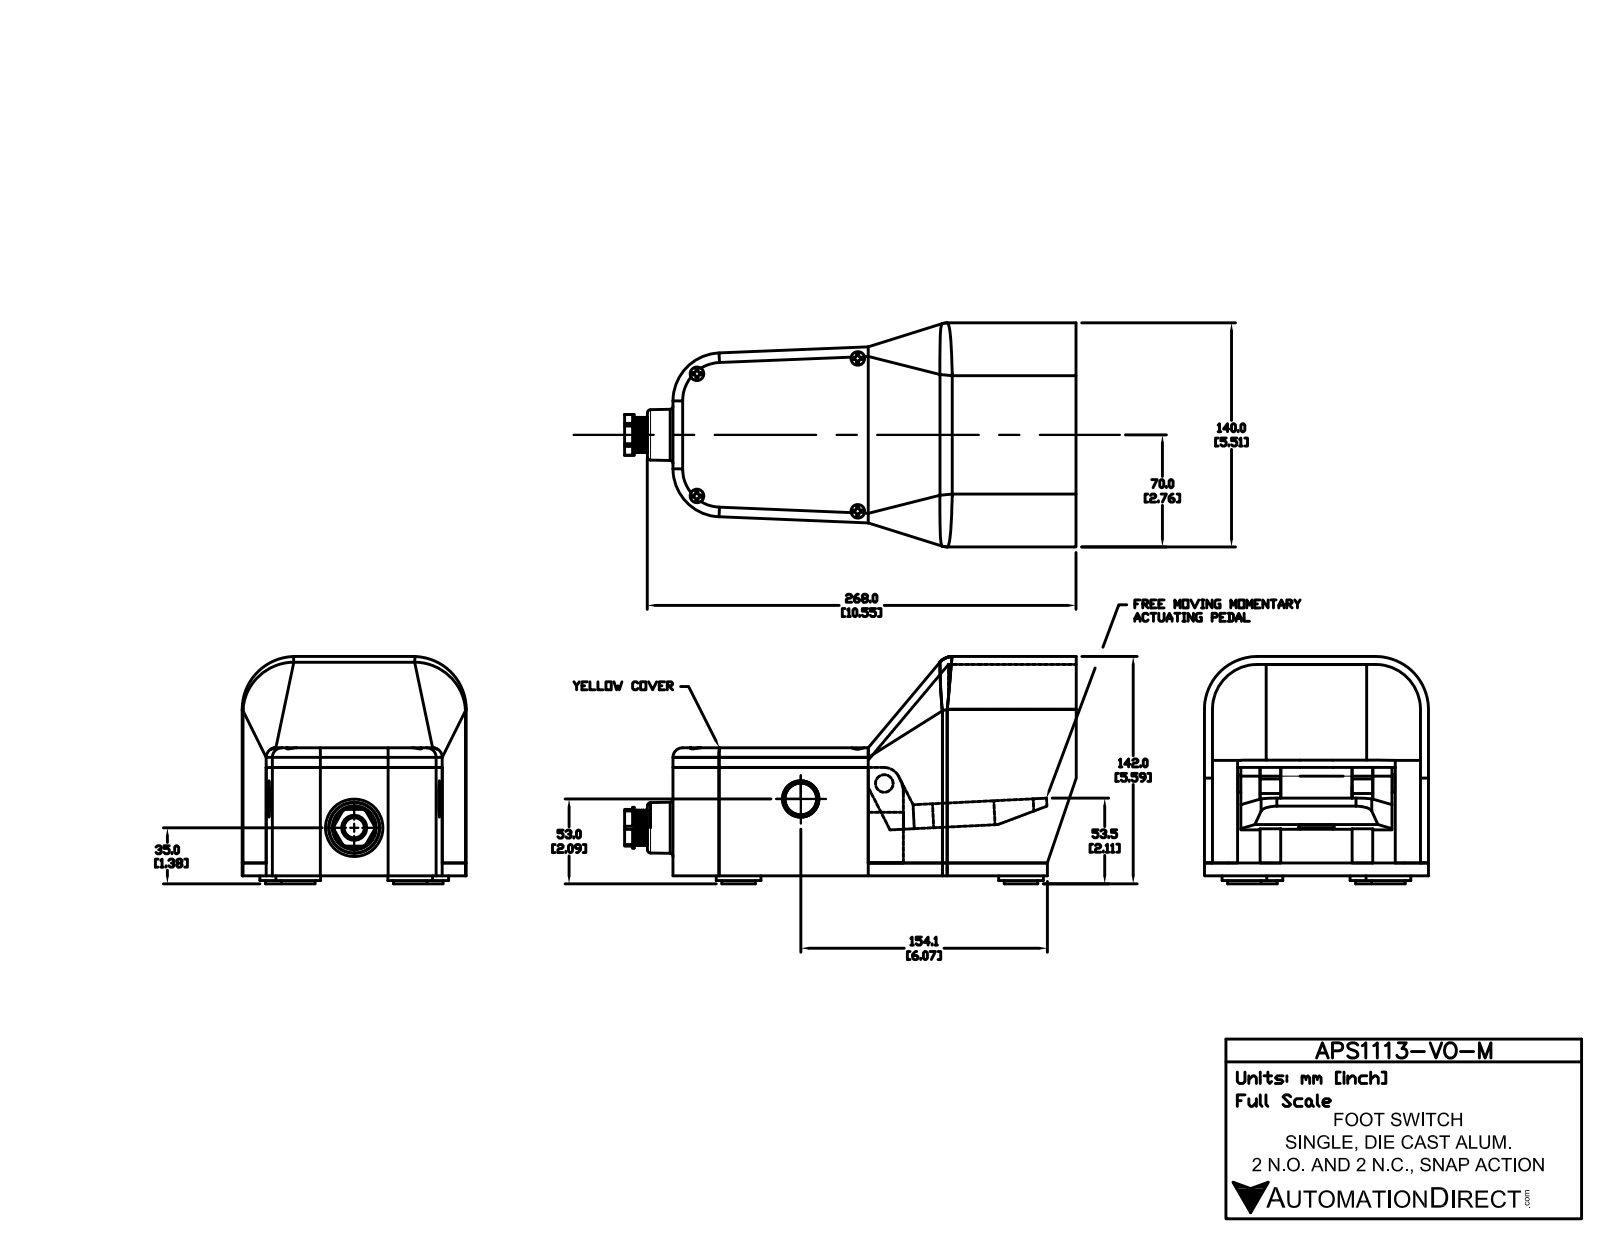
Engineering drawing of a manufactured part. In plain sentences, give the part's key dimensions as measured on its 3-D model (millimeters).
The part is named "APS1113-V0-M". Its 3-D file was written by "SolidWorks 2015 (AUTOMOTIVE_DESIGN)". It is 18 solids with 361 faces: 214 planar, 91 cylindrical and 56 other. Overall it measures 282.25 by 142 by 140 millimeters. Its volume is 1 541 000 cubic millimeters and its surface area 267 977 square millimeters. Round holes: 4 of diameter 8.5, 2 of diameter 22.75, 1 of diameter 12.65, 1 of diameter 15.6. Round bosses or shafts: 4 of diameter 28, 4 of diameter 21, 2 of diameter 19.87, 1 of diameter 25.5, 1 of diameter 22, 1 of diameter 11. Partial cylindrical surfaces (rounded edges, fillets, slot ends): 16 of radius 1, 6 of radius 10, 3 of radius 5.99, 2 of radius 28, 2 of radius 30, 2 of radius 33, 1 of radius 20. The main face-to-face distances are 5, 135, 8, 59.64, 67.67, 59.67, 67.64, 140, 80, 72. The hole center spacings are 101, 132.24, 76.3, 95.5.
